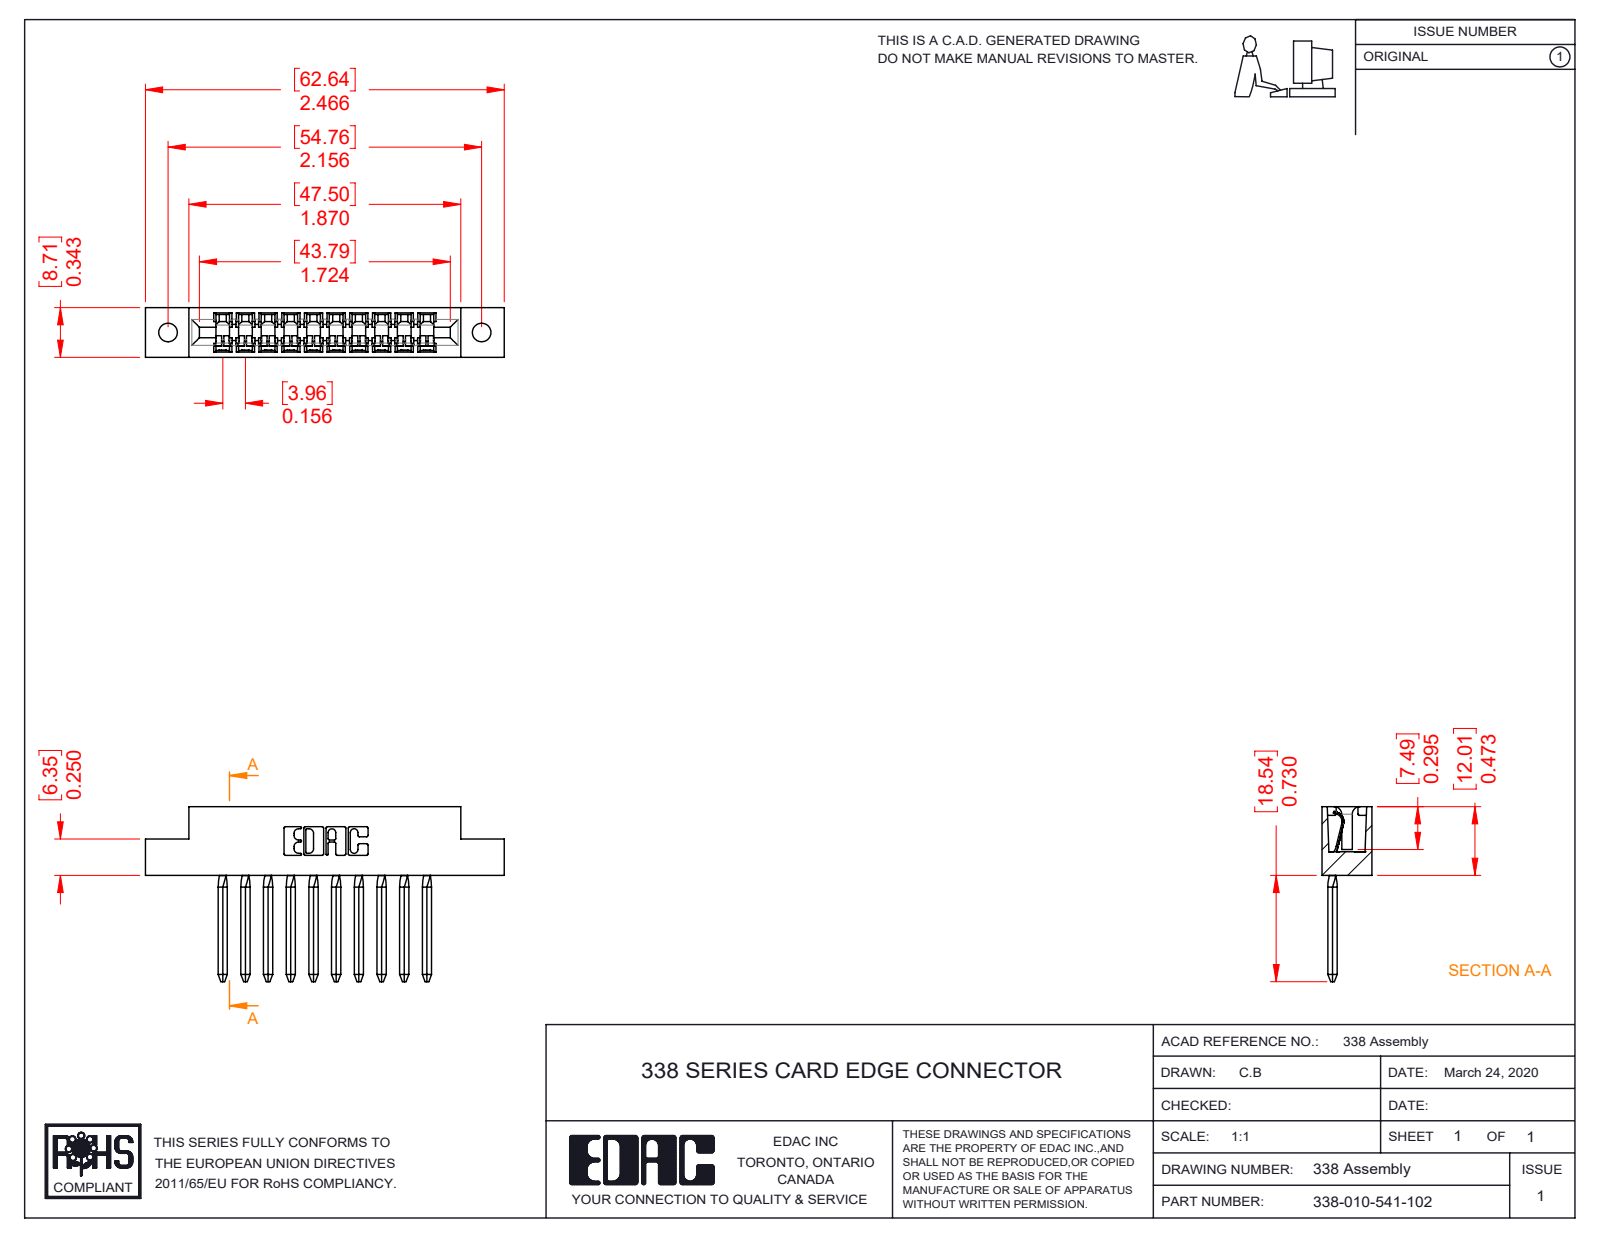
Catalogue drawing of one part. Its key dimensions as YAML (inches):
part_name: "338-290-001_541; 338-010-541-102; 338-210-001_338-210-010-002"
step_written_by: "SolidWorks 2016 (CONFIG_CONTROL_DESIGN)"
units: inches
bodies: {solids: 11, faces: 1024, planar: 700, cylindrical: 284, other: 40}
overall_size: [2.466, 1.203, 0.343]
volume: 0.262
surface_area: 9.526
round_holes:
  - {diameter: 0.128, count: 2}
partial_cylinders:
  - {radius: 0.025, count: 42}
  - {radius: 0.01, count: 22}
  - {radius: 0.008, count: 10}
  - {radius: 0.055, count: 8}
  - {radius: 0.067, count: 8}
  - {radius: 0.1, count: 8}
  - {radius: 0.007, count: 6}
  - {radius: 0.031, count: 6}
face_to_face_distances: [0.343, 0.156, 0.11, 0.25, 0.045, 0.624, 0.468, 0.221, 0.312, 0.312]
hole_center_spacings: [2.156]
